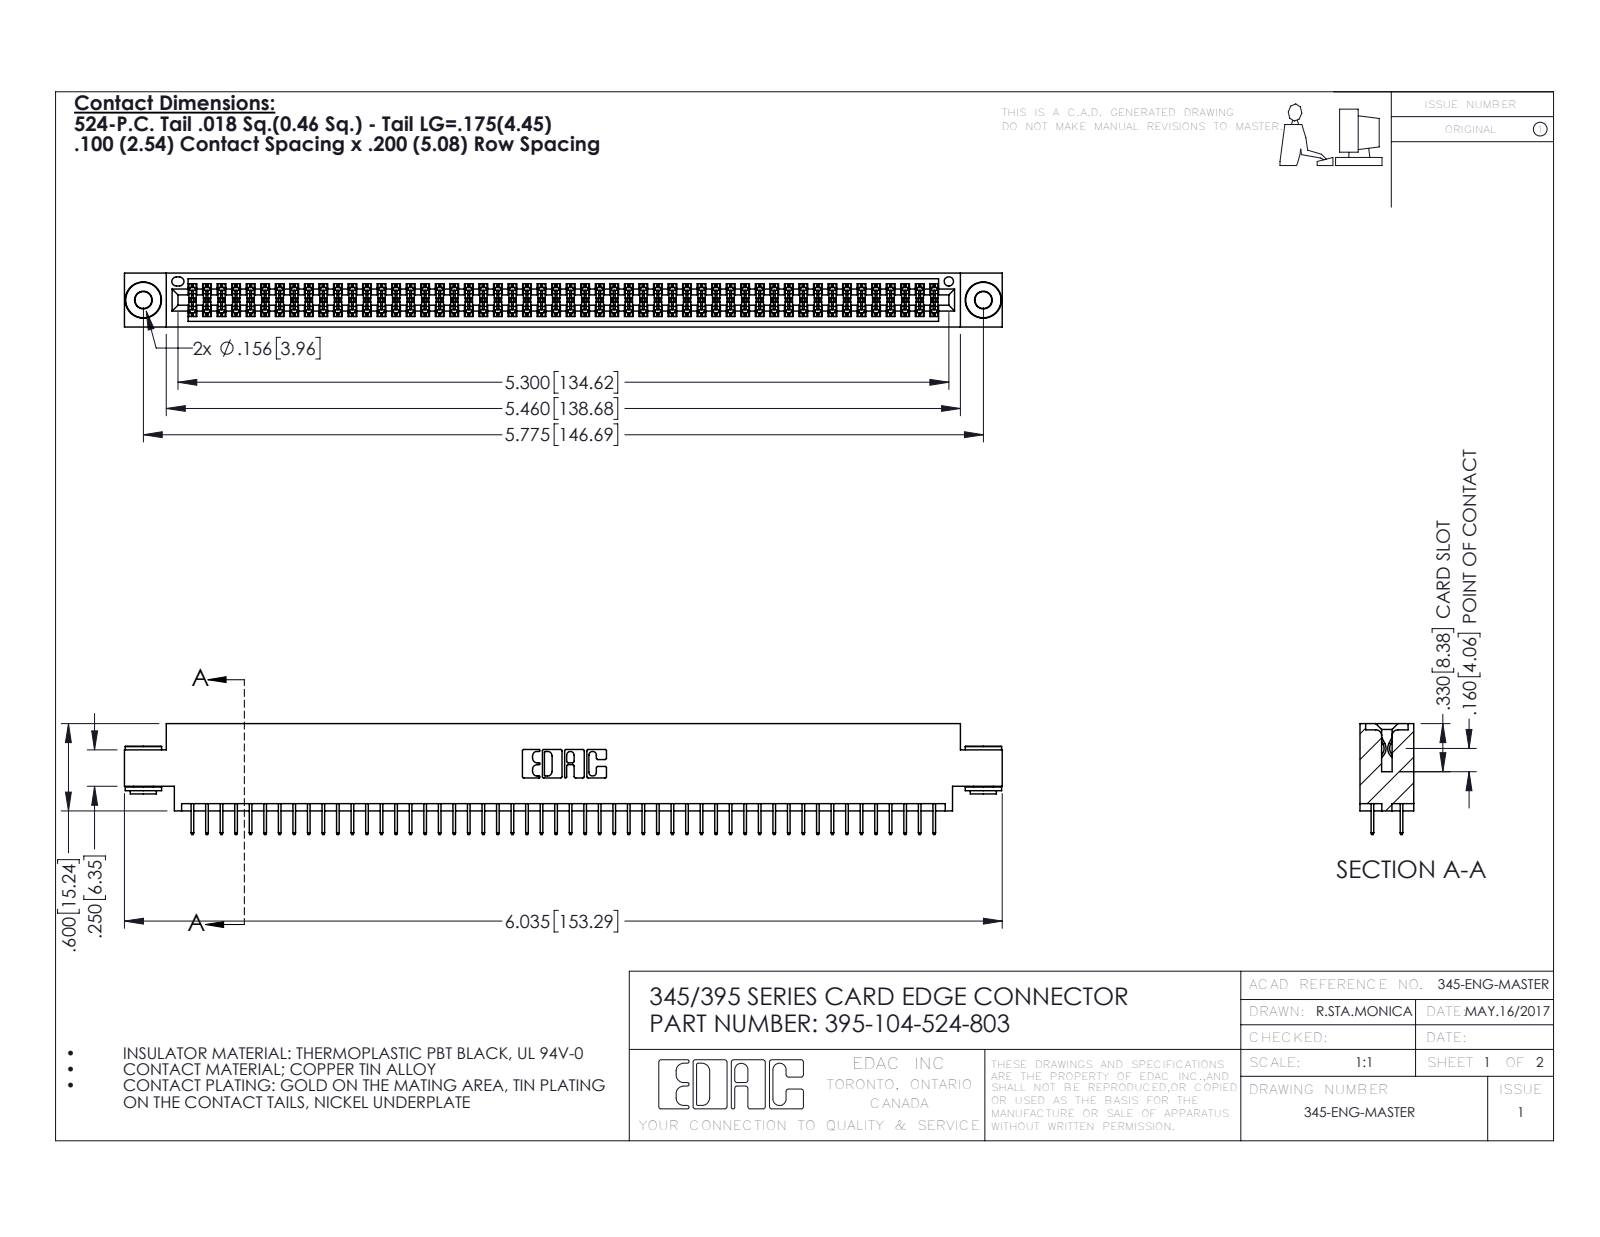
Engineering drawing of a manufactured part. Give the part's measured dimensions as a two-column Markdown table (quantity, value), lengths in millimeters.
| quantity | value |
| --- | --- |
| part name | 345 Part_0.170 Offset - 0.156 Dia-TH; 395-104-524-803; 345-292-001_345-293-124; 345-250-002_345-250-002-102 |
| STEP written by | SolidWorks 2016 (CONFIG_CONTROL_DESIGN) |
| units | millimeters |
| bodies | 107 solids, 5784 faces (4150 planar, 1626 cylindrical, 8 other) |
| overall size | 153.3 × 19.4 × 9.4 |
| volume | 14 700 mm³ |
| surface area | 21 900 mm² |
| round holes (diameter × count) | 2.9 × 2, 4 × 2, 1.6 × 1 |
| round bosses / shafts (diameter × count) | 6.4 × 2, 4.6 × 2, 3.5 × 2 |
| partial cylindrical surfaces (radius × count) | 0.2 × 156, 0.3 × 22, 0.2 × 6, 0.8 × 6, 0.7 × 3, 0.4 × 2, 0.5 × 2, 0.6 × 2 |
| main face-to-face distances | 1.8, 7.6, 9.4, 5.1, 2.5, 6.9, 0.6, 5.7, 4.4, 1.8 |
| hole center spacings | 6.9, 140.7, 146.7 |
